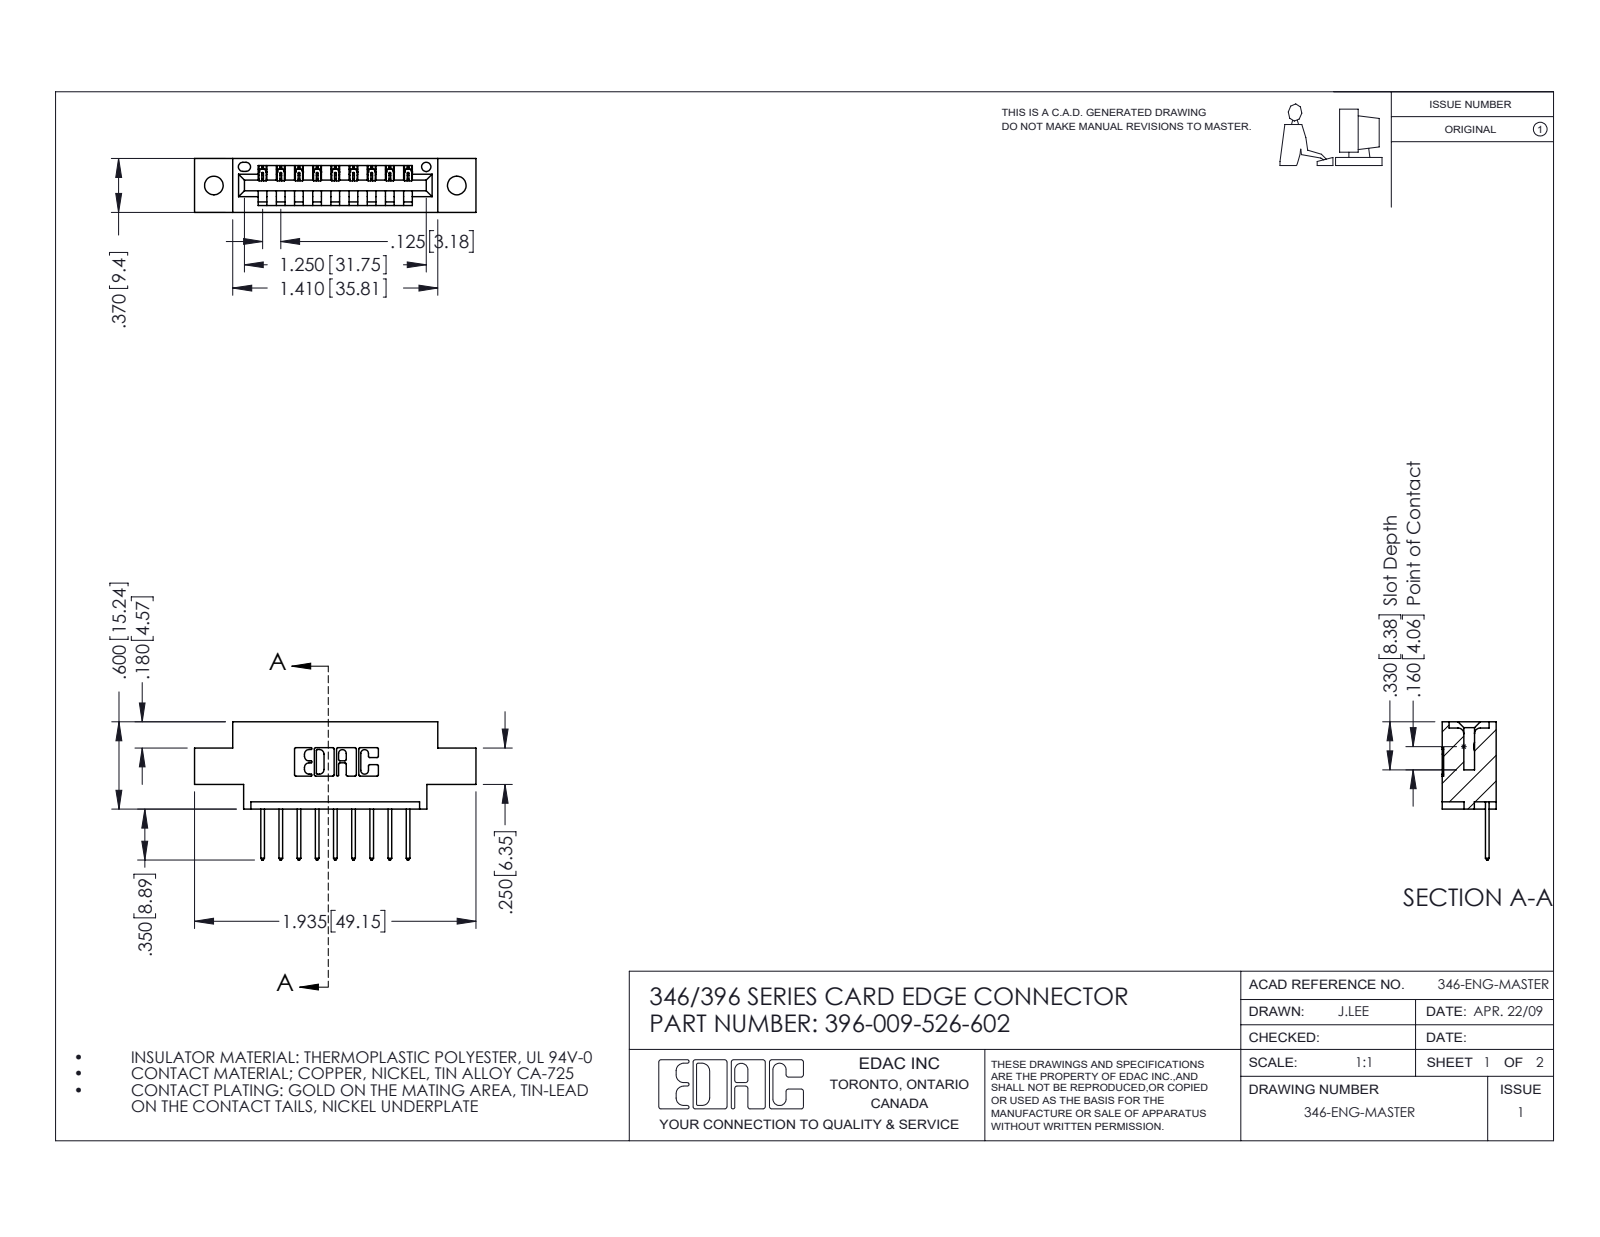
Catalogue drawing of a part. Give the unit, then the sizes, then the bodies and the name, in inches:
Units: inches
Overall size (bounding box): 1.935 × 0.95 × 0.37
Round holes (diameter × count): ⌀0.128 ×2, ⌀0.064 ×1
Partial cylindrical surfaces — rounded edges, fillets, slot ends (radius × count): R0.01 ×22, R0.006 ×18, R0.01 ×18, R0.007 ×6, R0.031 ×6, R0.026 ×3, R0.031 ×2, R0.04 ×2
Main face-to-face distances: 0.25, 0.37, 0.048, 0.322, 0.072, 0.298, 0.025, 0.148, 0.222, 0.1
Hole centre spacings: 0.246, 1.465, 1.67
Volume: 0.261 in³ · Surface area: 7.552 in²
Bodies: 10 solids, 648 faces (440 planar, 208 cylindrical, 0 other)
Part name (STEP PRODUCT): 396-009-526-602; 345-292-001_345-293-126; 346 Part_0.170 Offset - 0.128 Dia
STEP written by: SolidWorks 2016 (CONFIG_CONTROL_DESIGN)
